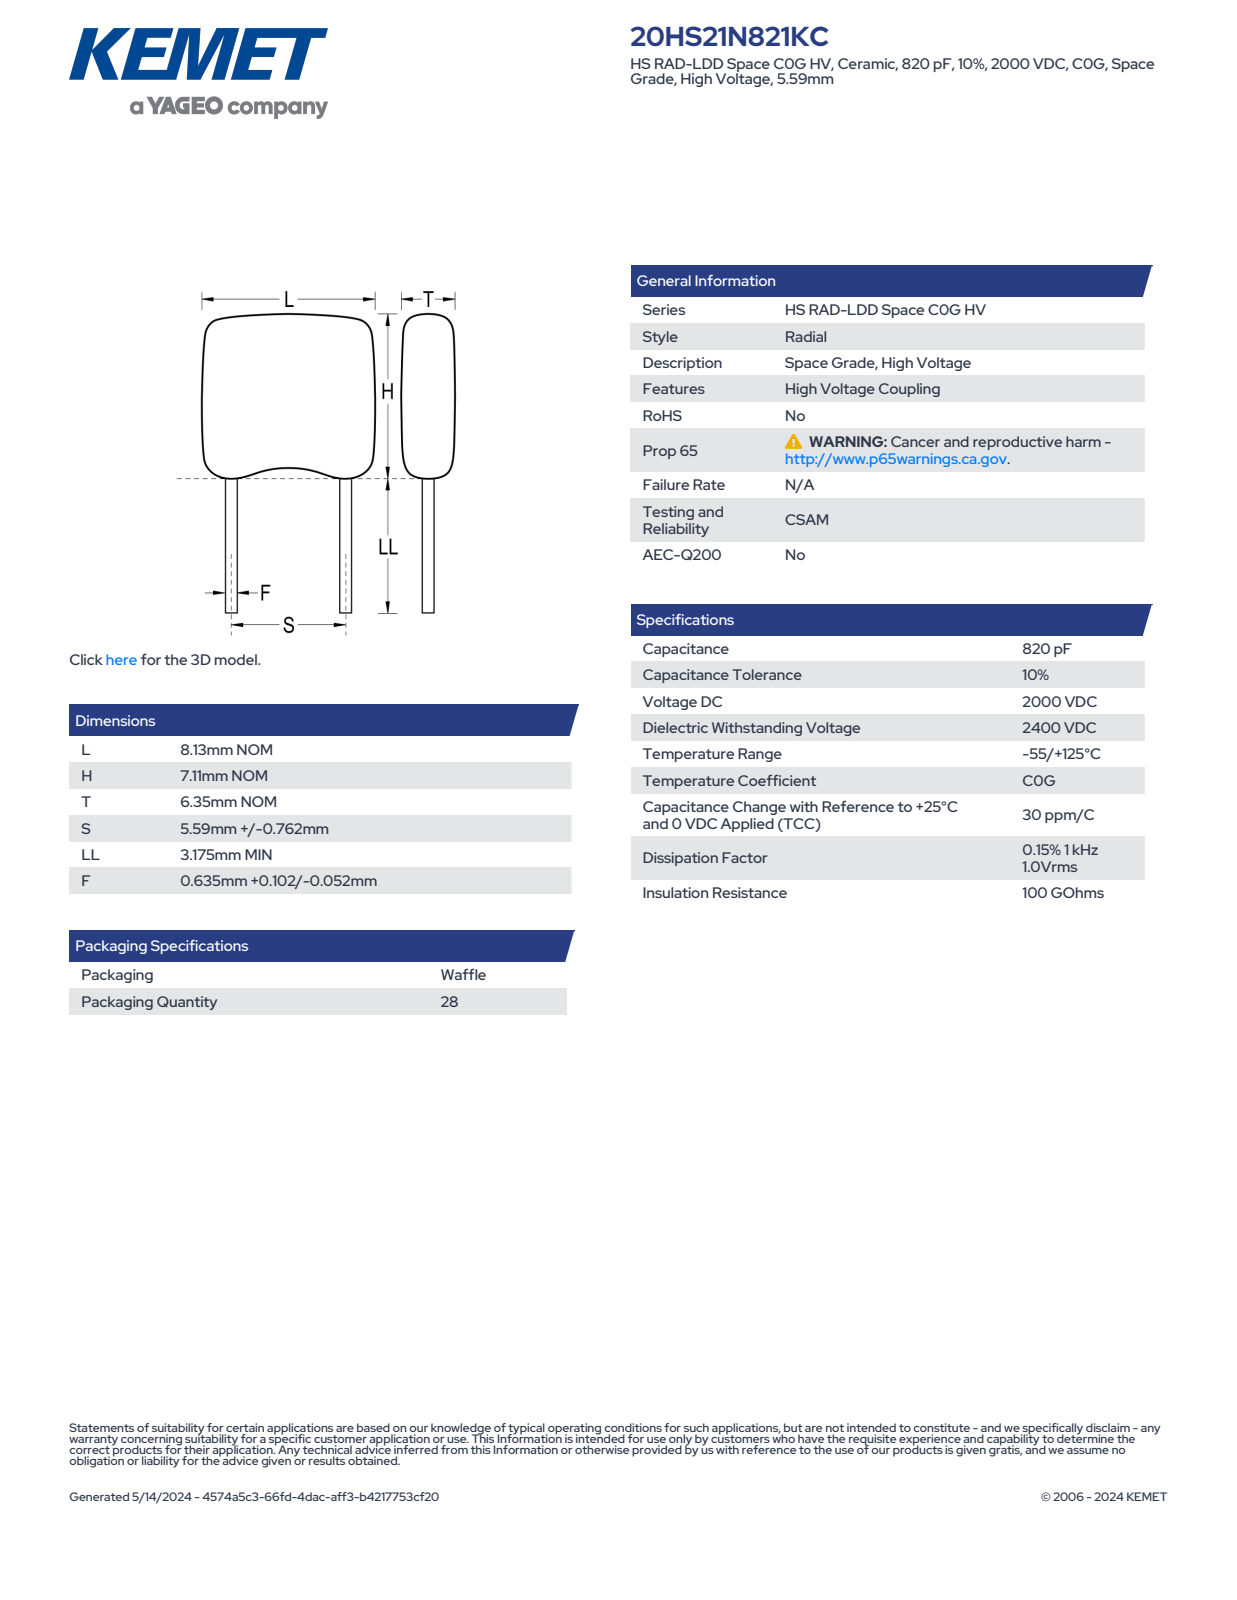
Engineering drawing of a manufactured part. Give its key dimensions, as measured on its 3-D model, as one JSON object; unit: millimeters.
{"part_name": "CCR_RMSTHP_HS21_L8.13H7.11T6.35S5.59LL3.175F0.737", "step_written_by": "SolidWorks 2021 (AUTOMOTIVE_DESIGN)", "units": "millimeters", "bodies": {"solids": 4, "faces": 83, "planar": 65, "cylindrical": 14, "other": 4}, "overall_size": [10.29, 8.13, 6.36], "volume_mm3": 361, "surface_area_mm2": 303, "round_bosses_or_shafts": [[0.74, 2]], "partial_cylinders_radius": [[0.75, 10]], "face_to_face_distances": [6.35, 7.11, 8.13, 3.18, 10.29, 0.78, 6.98, 3.8, 3.31, 6.2]}
